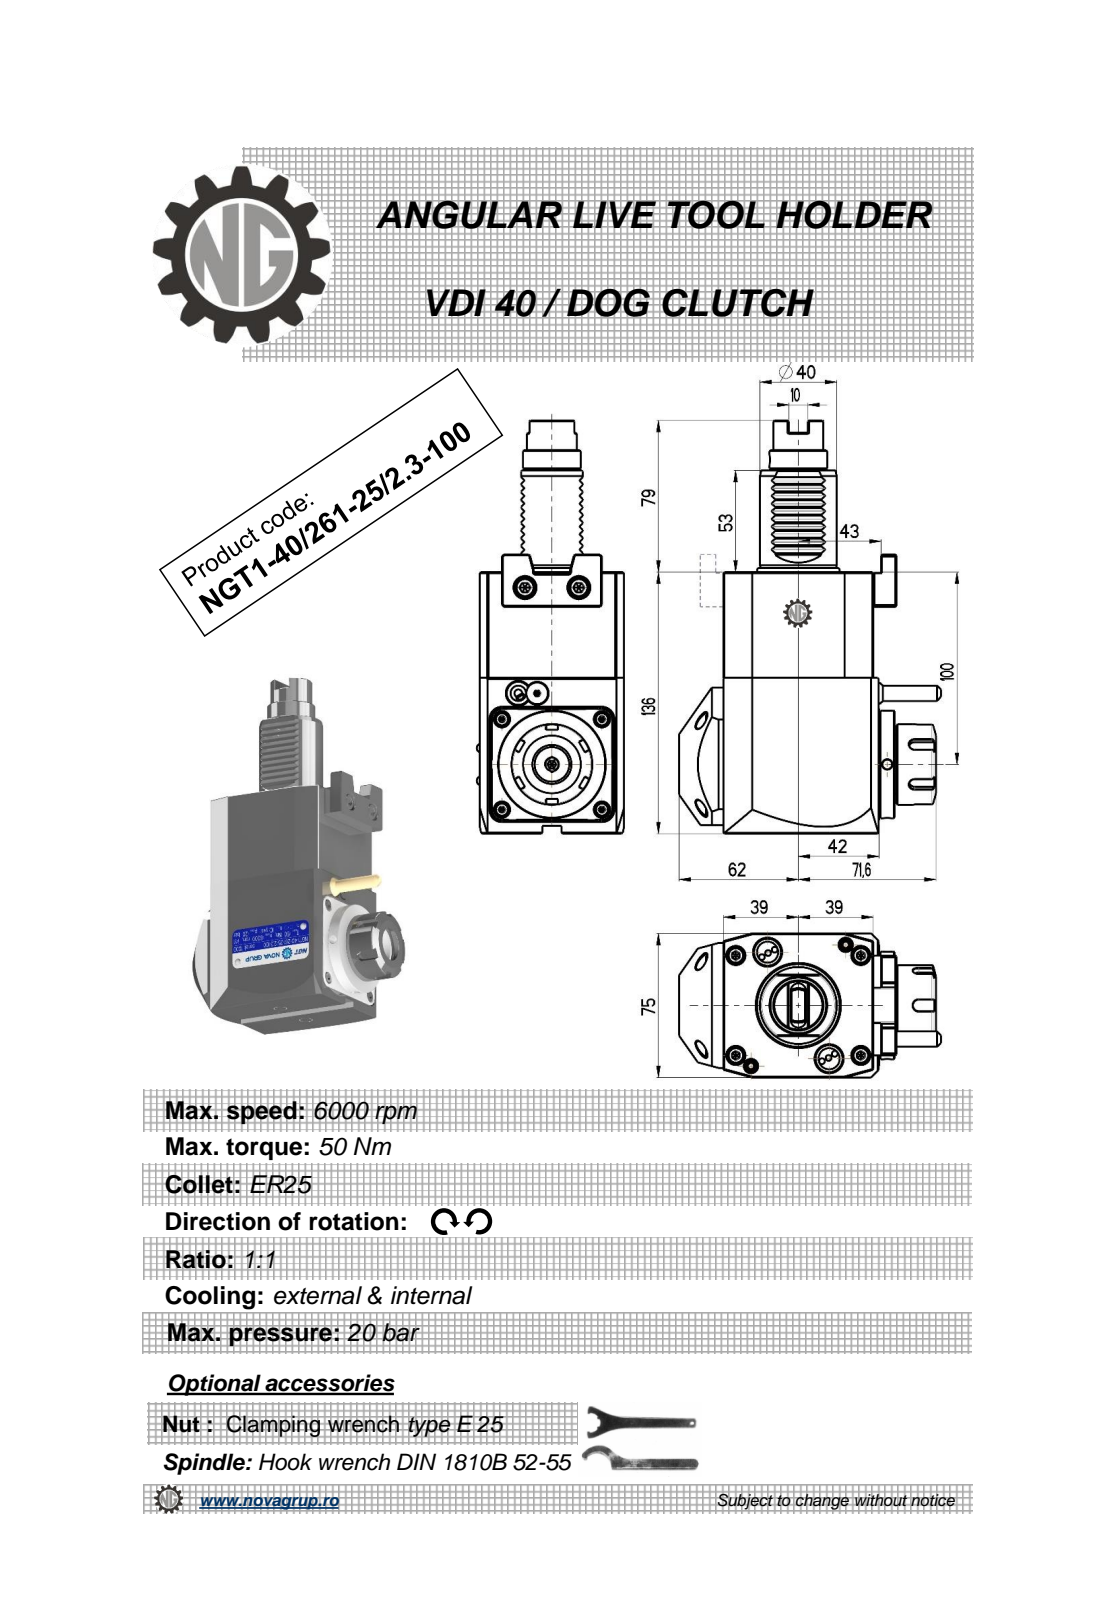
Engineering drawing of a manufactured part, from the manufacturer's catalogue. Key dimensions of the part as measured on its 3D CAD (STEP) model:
Part name (STEP PRODUCT): NGT1_40_261_25_2_3_100
STEP written by: PRO/ENGINEER BY PARAMETRIC TECHNOLOGY CORPORATION, 2010280 (CONFIG_CONTROL_DESIGN)
Units: millimetres
Bodies: 1 solid, 435 faces (227 planar, 77 cylindrical, 131 other)
Overall size (bounding box): 215 × 136.14 × 75
Volume: 995 166 mm³ · Surface area: 77 116 mm²
Round holes (diameter × count): ⌀5 ×3, ⌀3 ×1, ⌀4.2 ×1, ⌀20.3 ×1
Round bosses / shafts (diameter × count): ⌀56 ×1, ⌀43 ×1, ⌀42 ×1, ⌀40 ×1, ⌀33 ×1, ⌀30 ×1, ⌀26 ×1, ⌀11.2 ×1
Partial cylindrical surfaces — rounded edges, fillets, slot ends (radius × count): R0.3 ×20, R0.22 ×6, R3 ×5, R0.5 ×2, R1 ×2, R12.5 ×1, R40 ×1
Main face-to-face distances: 75, 136, 78, 81, 0.5, 3, 11, 8, 1, 8.2
Hole centre spacings: 40.93, 122.75, 158.5
